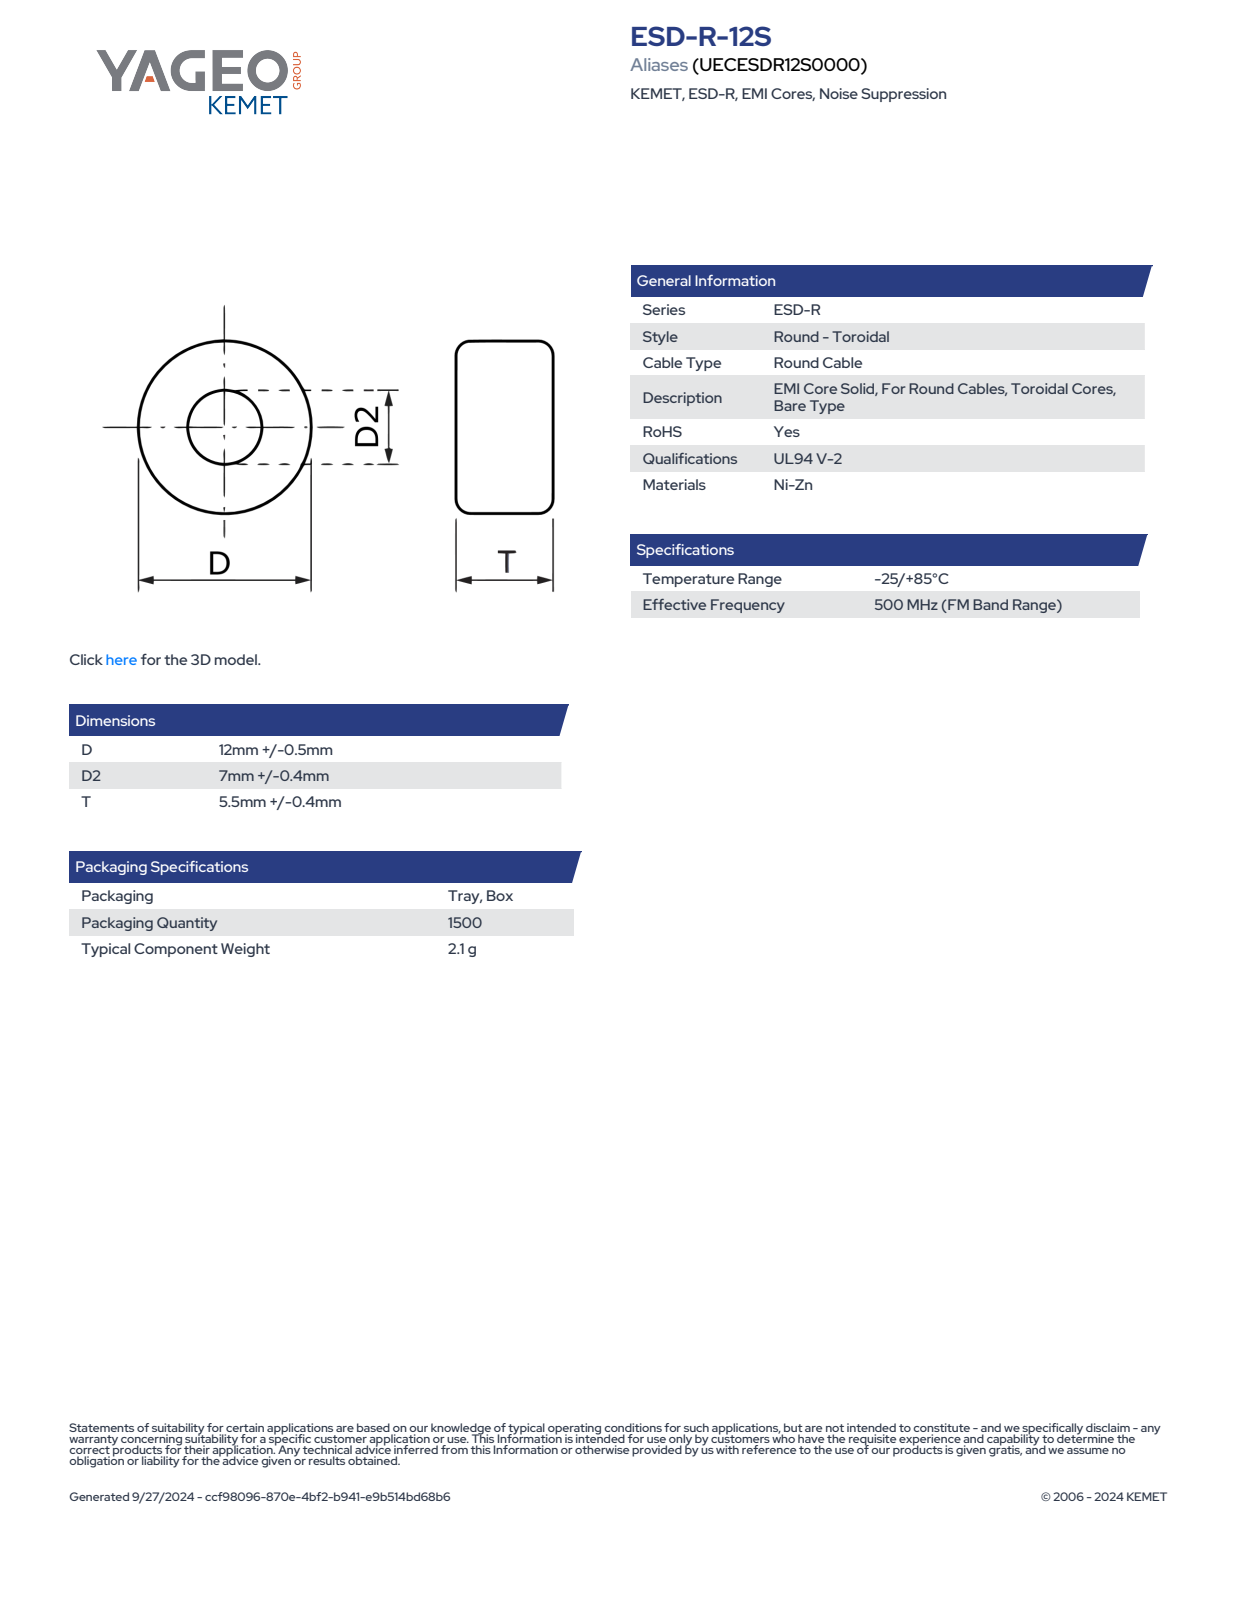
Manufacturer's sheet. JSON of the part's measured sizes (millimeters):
{"part_name": "EC_KBC_D12.5D27T5.9", "step_written_by": "SolidWorks 2021 (AUTOMOTIVE_DESIGN)", "units": "millimeters", "bodies": {"solids": 1, "faces": 66, "planar": 24, "cylindrical": 7, "other": 35}, "overall_size": [12.51, 12.5, 5.9], "volume_mm3": 494, "surface_area_mm2": 518, "round_holes": [[7, 1]], "round_bosses_or_shafts": [[12.5, 1]], "partial_cylinders_radius": [[6.26, 1]], "face_to_face_distances": [5.9, 2.1, 3.8, 1.7, 0.32, 2.42, 3.48, 1.38, 1.06, 3.16]}
